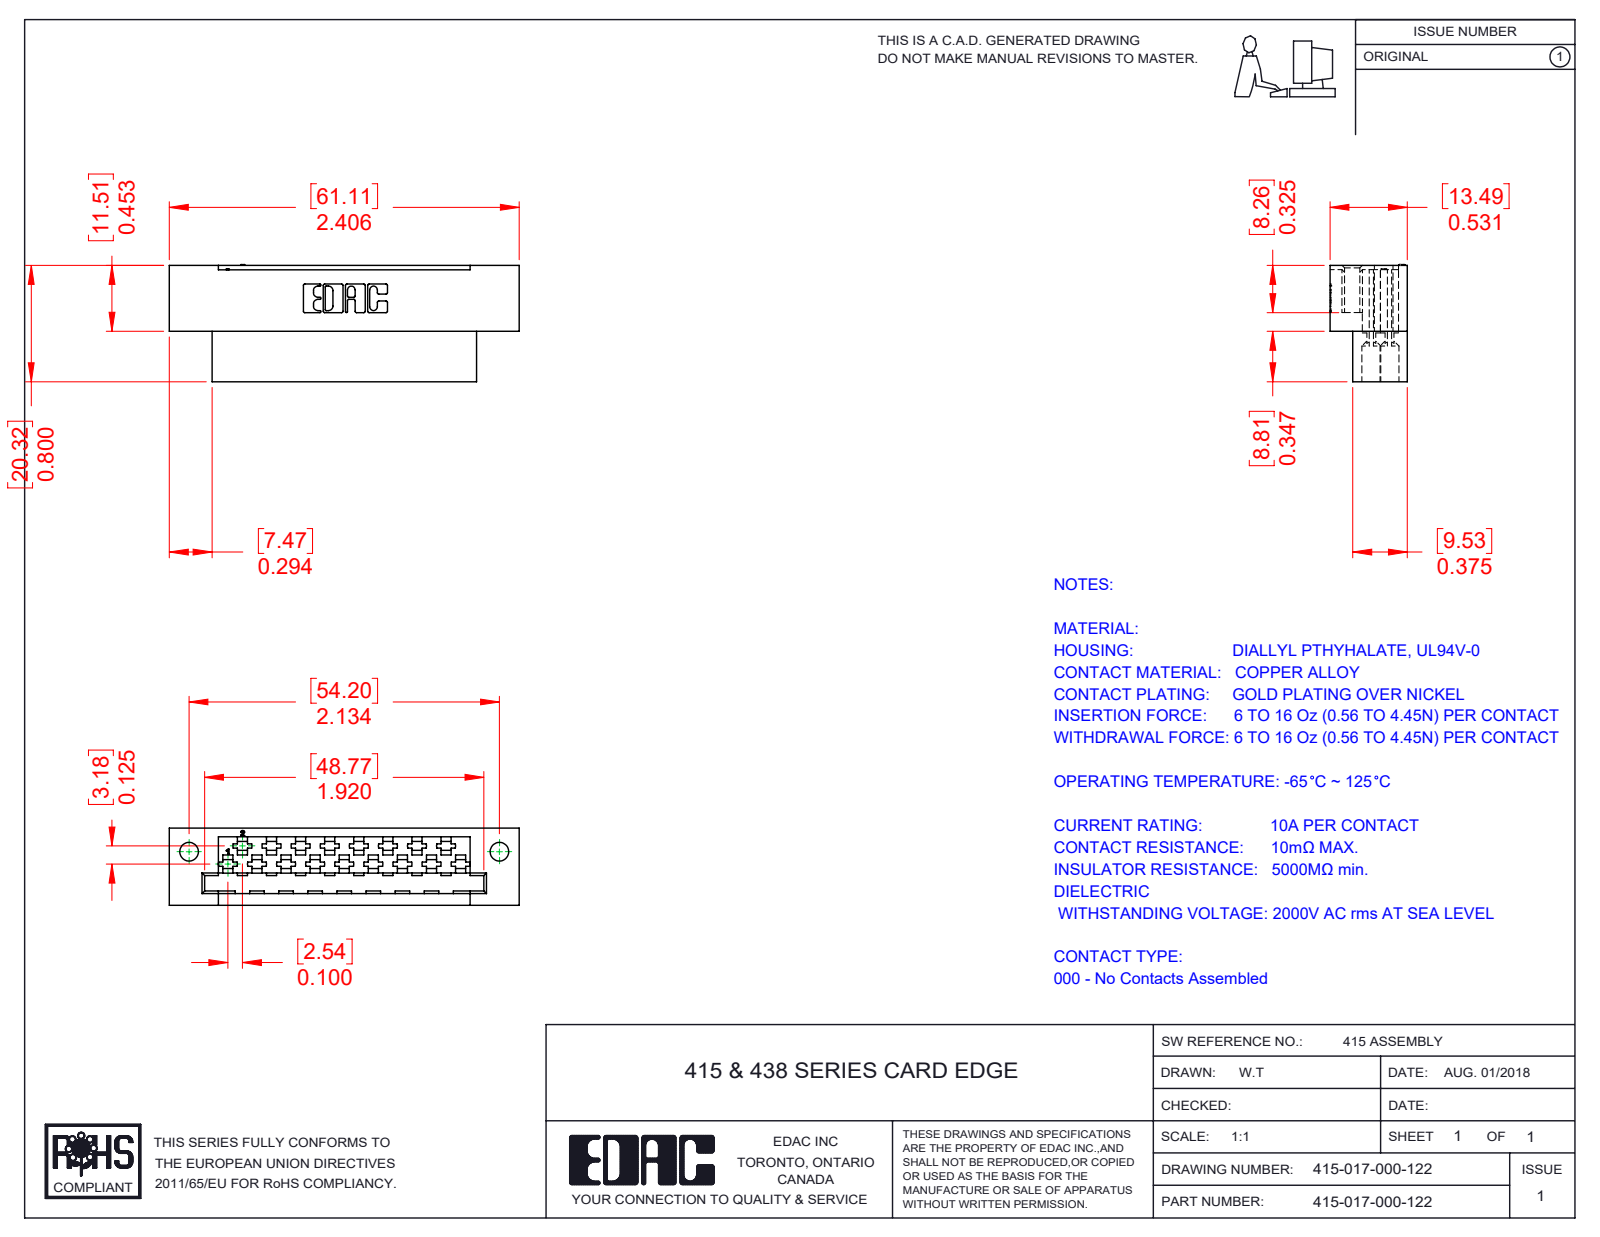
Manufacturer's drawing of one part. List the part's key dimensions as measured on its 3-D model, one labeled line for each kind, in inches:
Part name (STEP PRODUCT): 415-017-000-122; 415-210-001_415-210-017-122
STEP written by: SolidWorks 2016 (CONFIG_CONTROL_DESIGN)
Units: inches
Bodies: 1 solid, 586 faces (435 planar, 78 cylindrical, 73 other)
Overall size (bounding box): 2.406 × 0.805 × 0.531
Volume: 0.566 in³ · Surface area: 13.81 in²
Round holes (diameter × count): ⌀0.13 ×17, ⌀0.128 ×2
Partial cylindrical surfaces — rounded edges, fillets, slot ends (radius × count): R0.01 ×22, R0.007 ×6, R0.031 ×6, R0.026 ×3
Main face-to-face distances: 0.531, 0.8, 0.375, 0.156, 0.2, 0.4, 0.048, 0.047, 0.029, 0.076
Hole centre spacings: 0.16, 0.2, 0.325, 0.4, 0.515, 0.6, 0.711, 0.8
